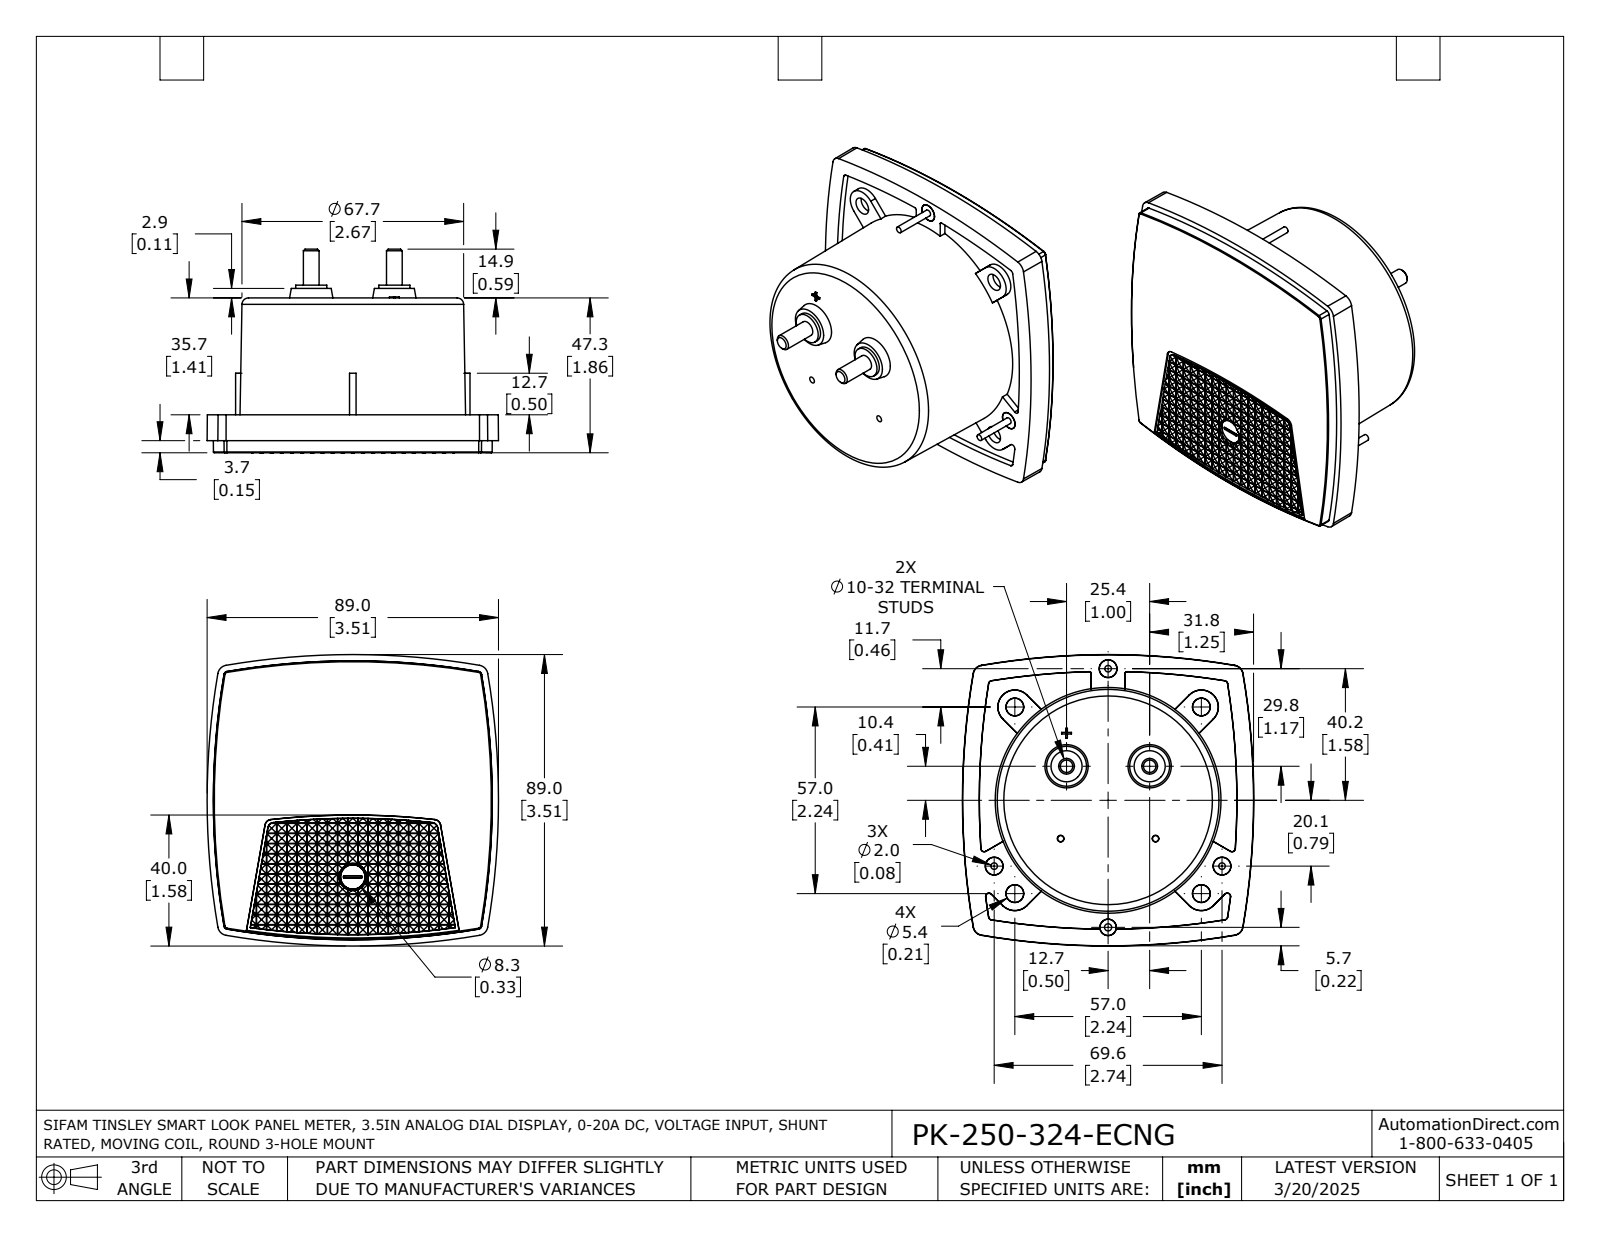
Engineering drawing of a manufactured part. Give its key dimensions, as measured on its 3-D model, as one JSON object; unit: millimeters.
{"part_name": "PK-250-324-ECNG", "step_written_by": "SolidWorks 2021 (AUTOMOTIVE_DESIGN)", "units": "millimeters", "bodies": {"solids": 1, "faces": 1078, "planar": 950, "cylindrical": 23, "other": 105}, "overall_size": [89, 89, 62.3], "volume_mm3": 212900, "surface_area_mm2": 28570, "round_holes": [[2.2, 1]], "round_bosses_or_shafts": [[5.4, 3], [2, 3], [9.5, 2], [4.8, 2]], "partial_cylinders_radius": [[227.6, 1]], "face_to_face_distances": [47.3, 35.7, 11.6, 2, 37.7, 9.6, 0.6, 2.4, 1.8, 3]}
